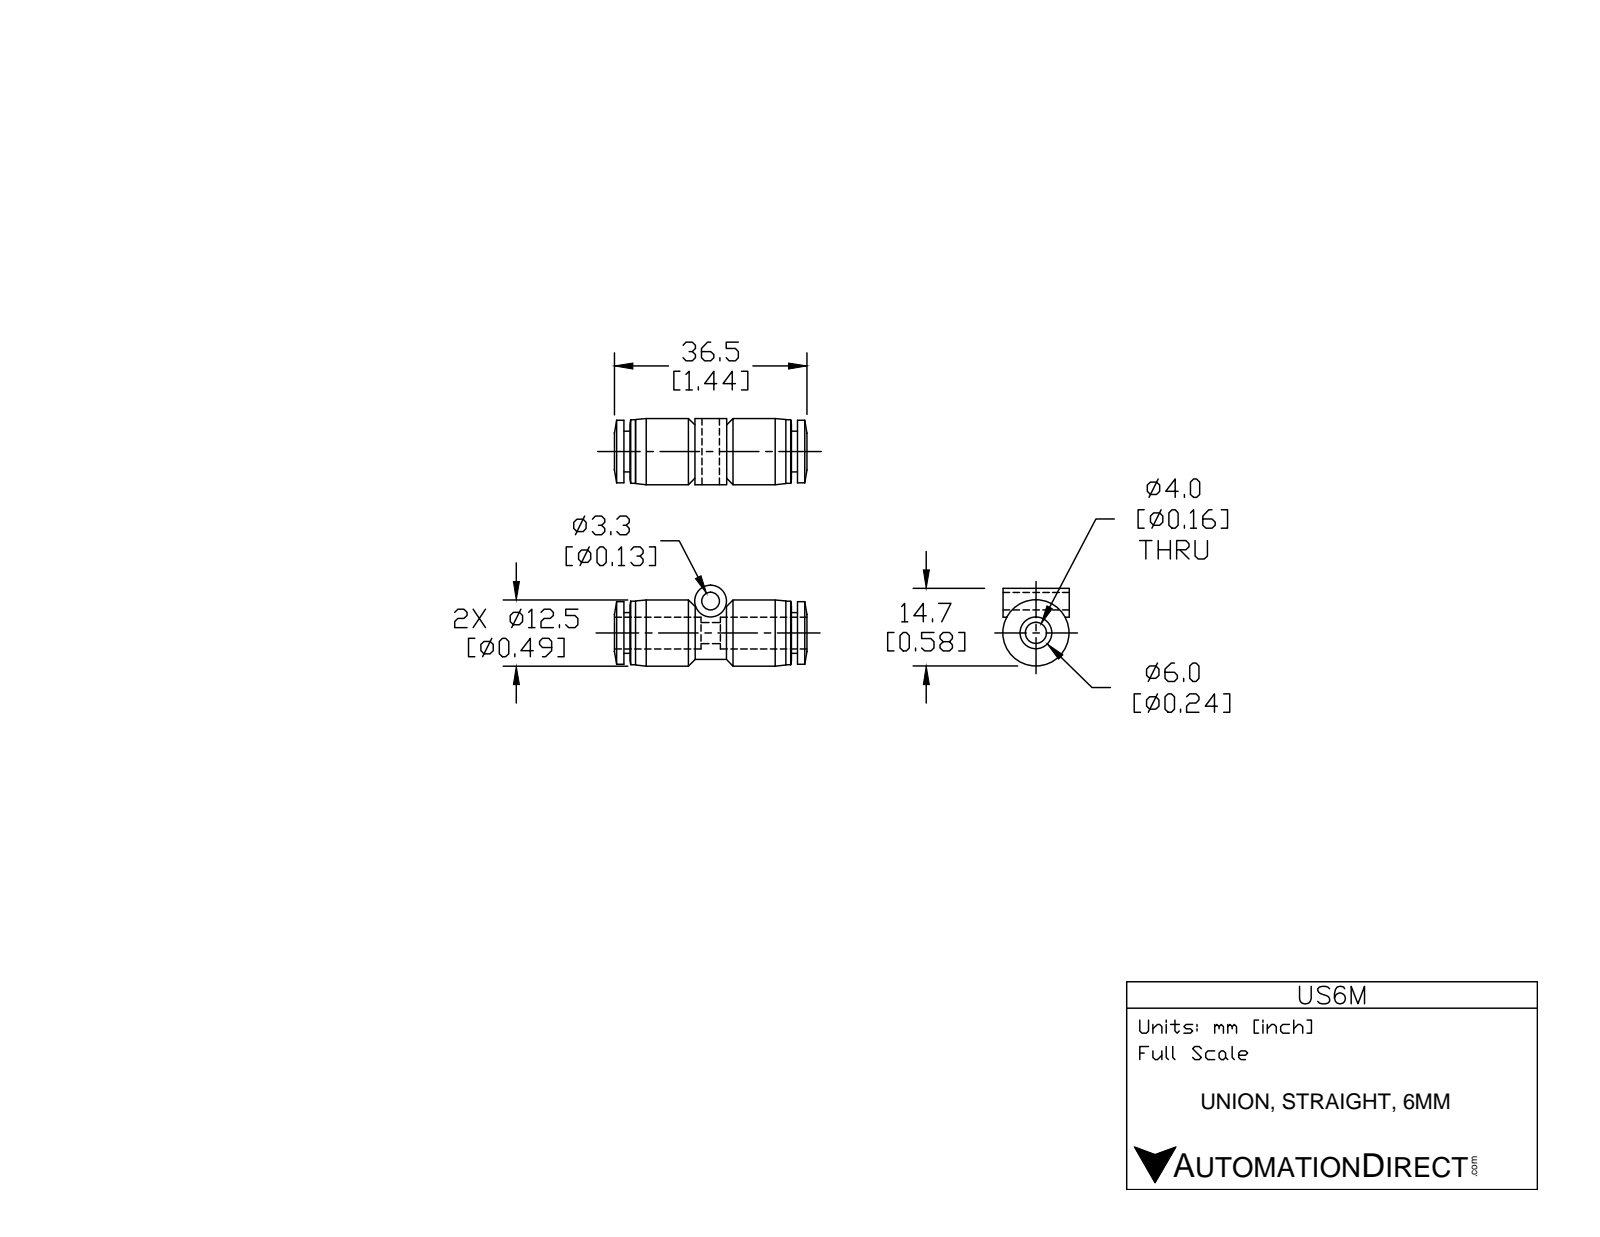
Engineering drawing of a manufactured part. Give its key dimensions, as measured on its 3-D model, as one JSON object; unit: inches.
{"part_name": "US6M", "step_written_by": "SolidWorks 2015 (AUTOMOTIVE_DESIGN)", "units": "inches", "bodies": {"solids": 1, "faces": 60, "planar": 12, "cylindrical": 28, "other": 20}, "overall_size": [1.433, 0.6, 0.492], "volume_in3": 0.181, "surface_area_in2": 4.312, "round_holes": [[0.13, 1], [0.197, 1], [0.248, 1]], "round_bosses_or_shafts": [[0.492, 1], [0.472, 1], [0.465, 1], [0.394, 1], [0.303, 1], [0.236, 1]], "face_to_face_distances": [0.045, 1.246, 1.291, 1.201, 0.575, 0.717, 0.53, 0.671, 0.492, 0.142]}
